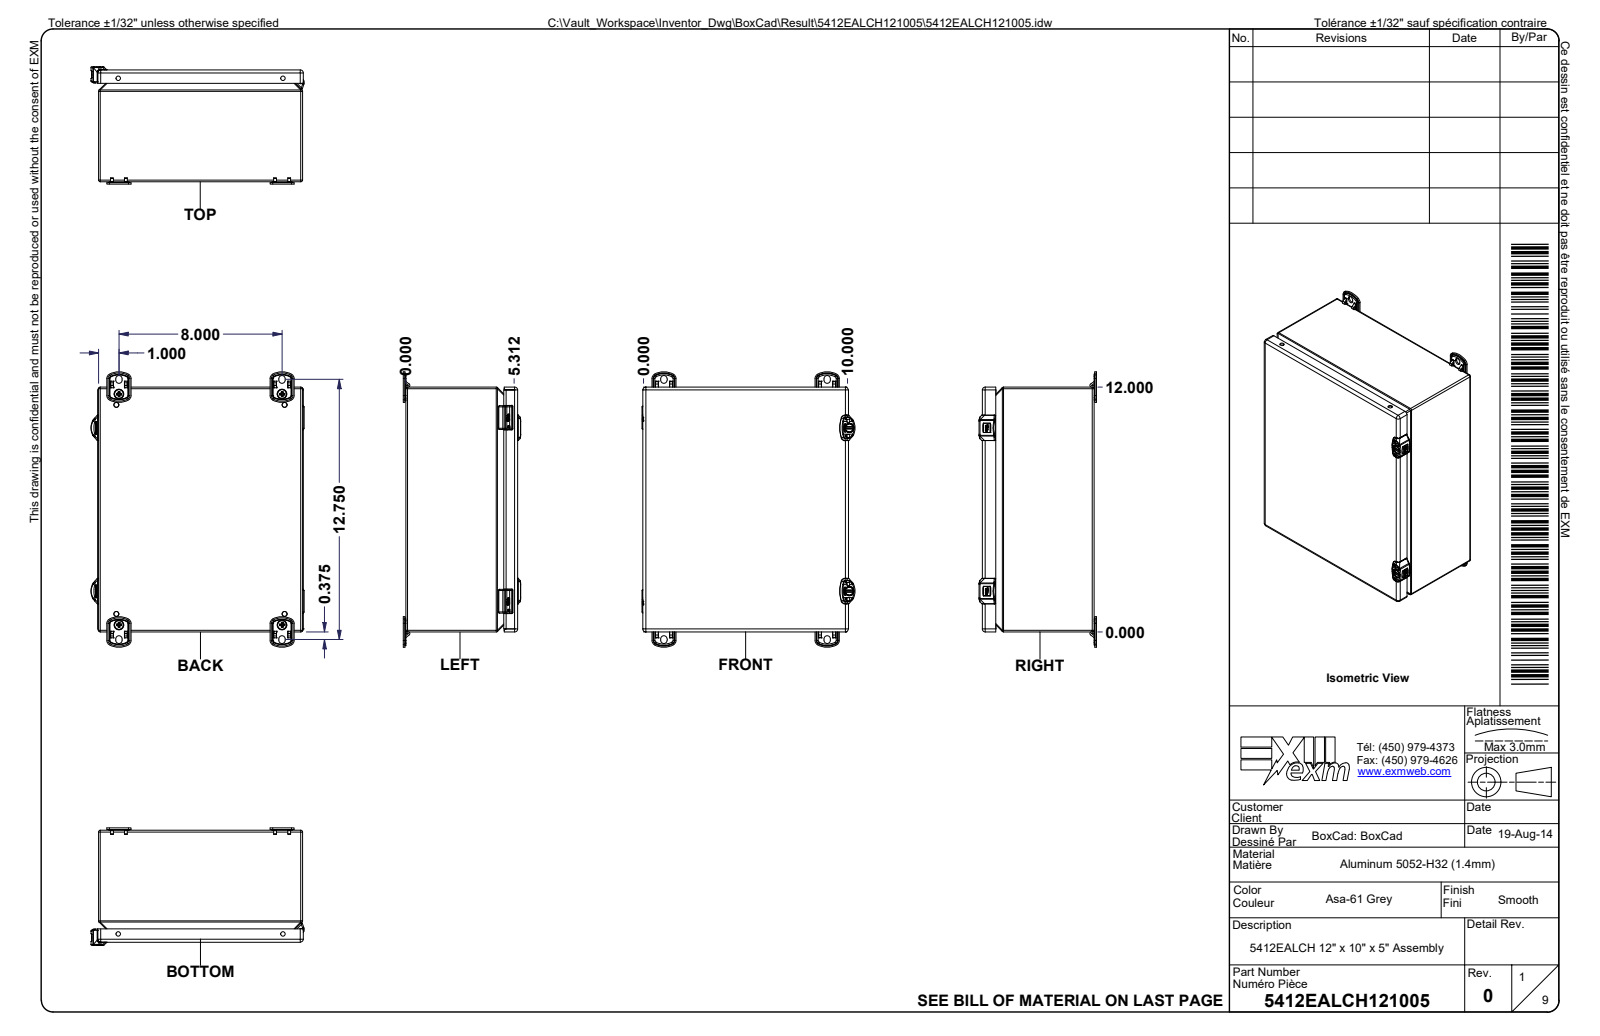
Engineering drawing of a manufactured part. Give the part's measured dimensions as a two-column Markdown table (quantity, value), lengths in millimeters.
| quantity | value |
| --- | --- |
| part name | 5412EALCH121005; 5412EALCH121005B; 5412EALCH121005B-P; RIVET_NUT_SS_M6_FH_CE (+8 more) |
| STEP written by | Autodesk Inventor 2024 (AUTOMOTIVE_DESIGN) |
| units | millimeters |
| bodies | 51 solids, 7011 faces (3177 planar, 1538 cylindrical, 2296 other) |
| overall size | 342.8 × 265.2 × 146.2 |
| volume | 615 000 mm³ |
| surface area | 858 700 mm² |
| round holes (diameter × count) | 5 × 4, 5 × 4, 6 × 4, 8.1 × 4, 5.1 × 3, 0.8 × 2, 4.2 × 2, 4.4 × 2, 5.5 × 2, 5.8 × 2, 6 × 2, 6.1 × 2 |
| round bosses / shafts (diameter × count) | 5.9 × 8, 12.7 × 4, 6 × 4, 5 × 3, 10.5 × 2, 10 × 2, 8.4 × 2, 7.6 × 2 |
| partial cylindrical surfaces (radius × count) | 0.2 × 224, 0.5 × 135, 0.1 × 97, 1 × 77, 0.3 × 63, 0.8 × 33, 2 × 30, 1.5 × 29 |
| main face-to-face distances | 1.3, 137.9, 136.5, 139.2, 252.7, 6, 7.7, 7.3, 130.5, 131.9 |
| hole center spacings | 13.9, 273.8, 342.9, 260.4, 206.8, 228.6, 233, 203.2 |
